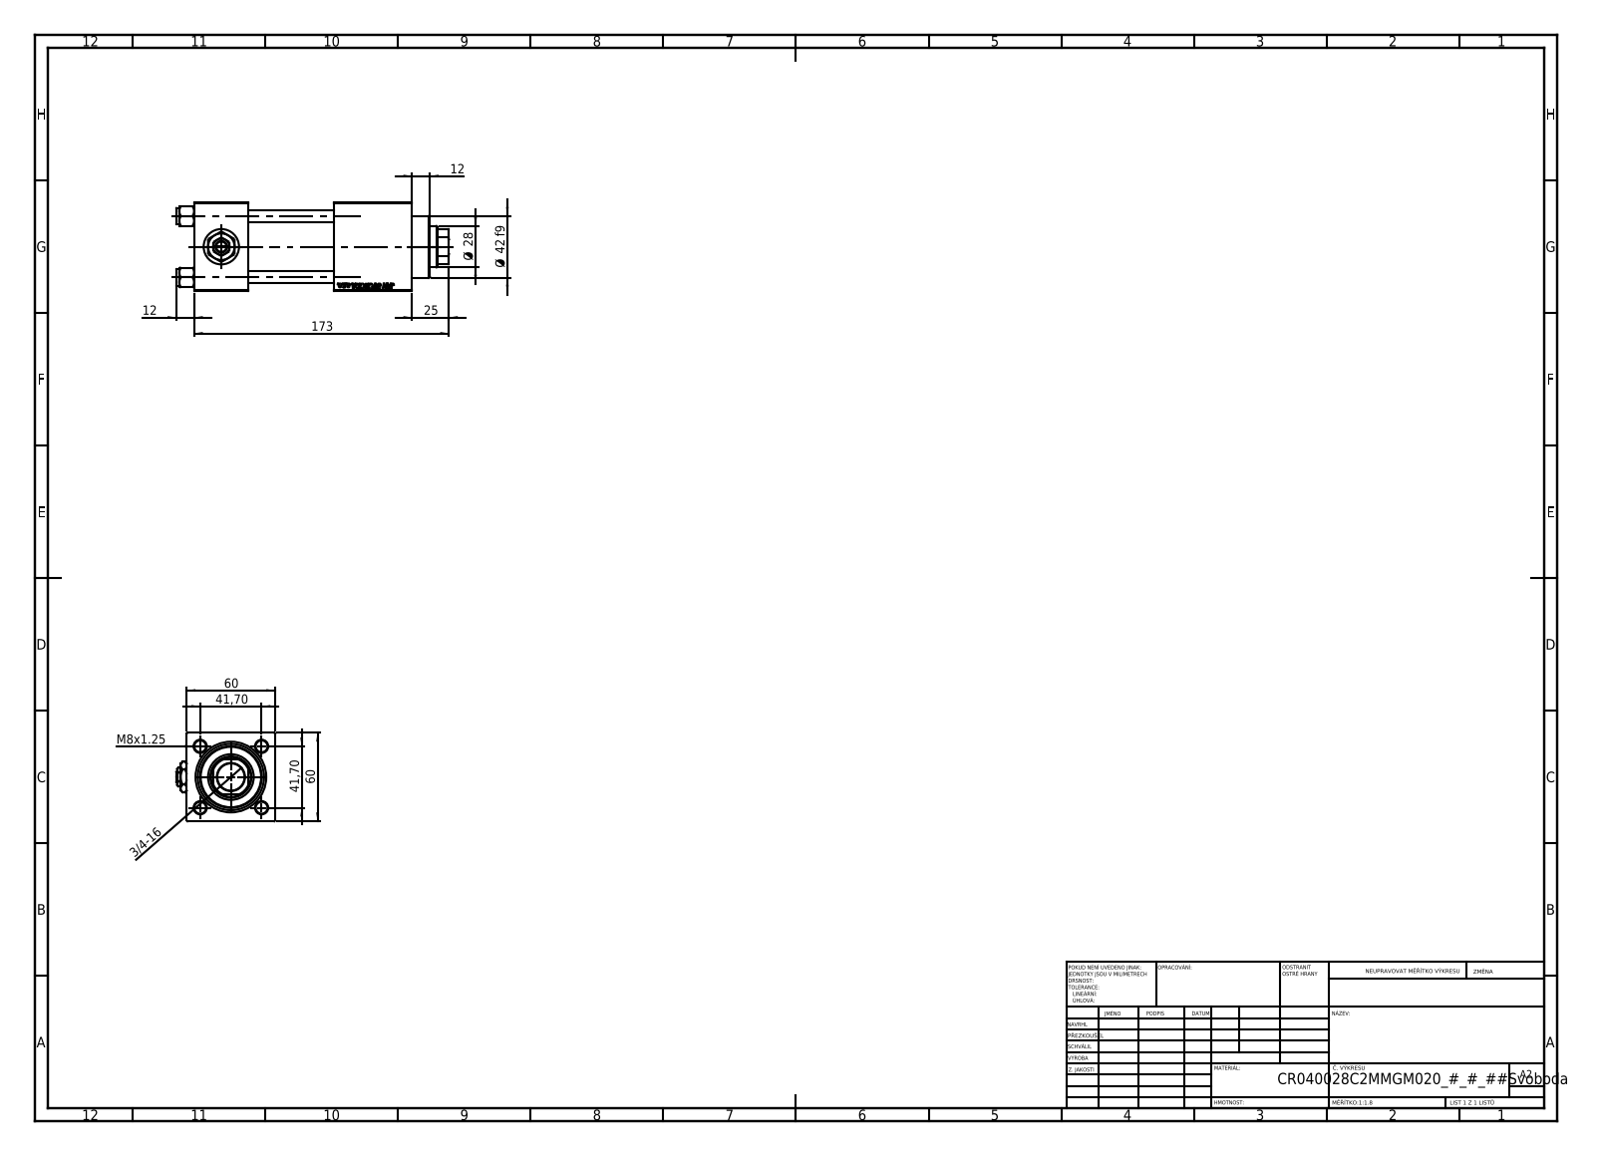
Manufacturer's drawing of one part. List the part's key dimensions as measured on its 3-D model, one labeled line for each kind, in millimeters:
Part name (STEP PRODUCT): V215_VC_A; V215CR_C_Body; V215CR_VCP_C; Zatka_pro_OIL_PORT (+2 more)
STEP written by: SolidWorks 2019 (CONFIG_CONTROL_DESIGN)
Units: millimetres
Bodies: 12 solids, 1202 faces (550 planar, 94 cylindrical, 558 other)
Overall size (bounding box): 185 × 67 × 60
Volume: 422 827 mm³ · Surface area: 113 084 mm²
Round holes (diameter × count): ⌀8 ×4, ⌀7 ×2, ⌀16.66 ×2, ⌀24 ×2, ⌀18.5 ×1, ⌀28 ×1, ⌀31 ×1, ⌀40 ×1, ⌀45 ×1
Round bosses / shafts (diameter × count): ⌀11 ×4, ⌀46 ×1, ⌀42 ×1
Partial cylindrical surfaces — rounded edges, fillets, slot ends (radius × count): R13.5 ×1
Main face-to-face distances: 60, 37, 58, 95, 53, 119.3, 82.3, 24.3, 148, 111
Hole centre spacings: 29.49, 41.7, 58.97, 92.5
